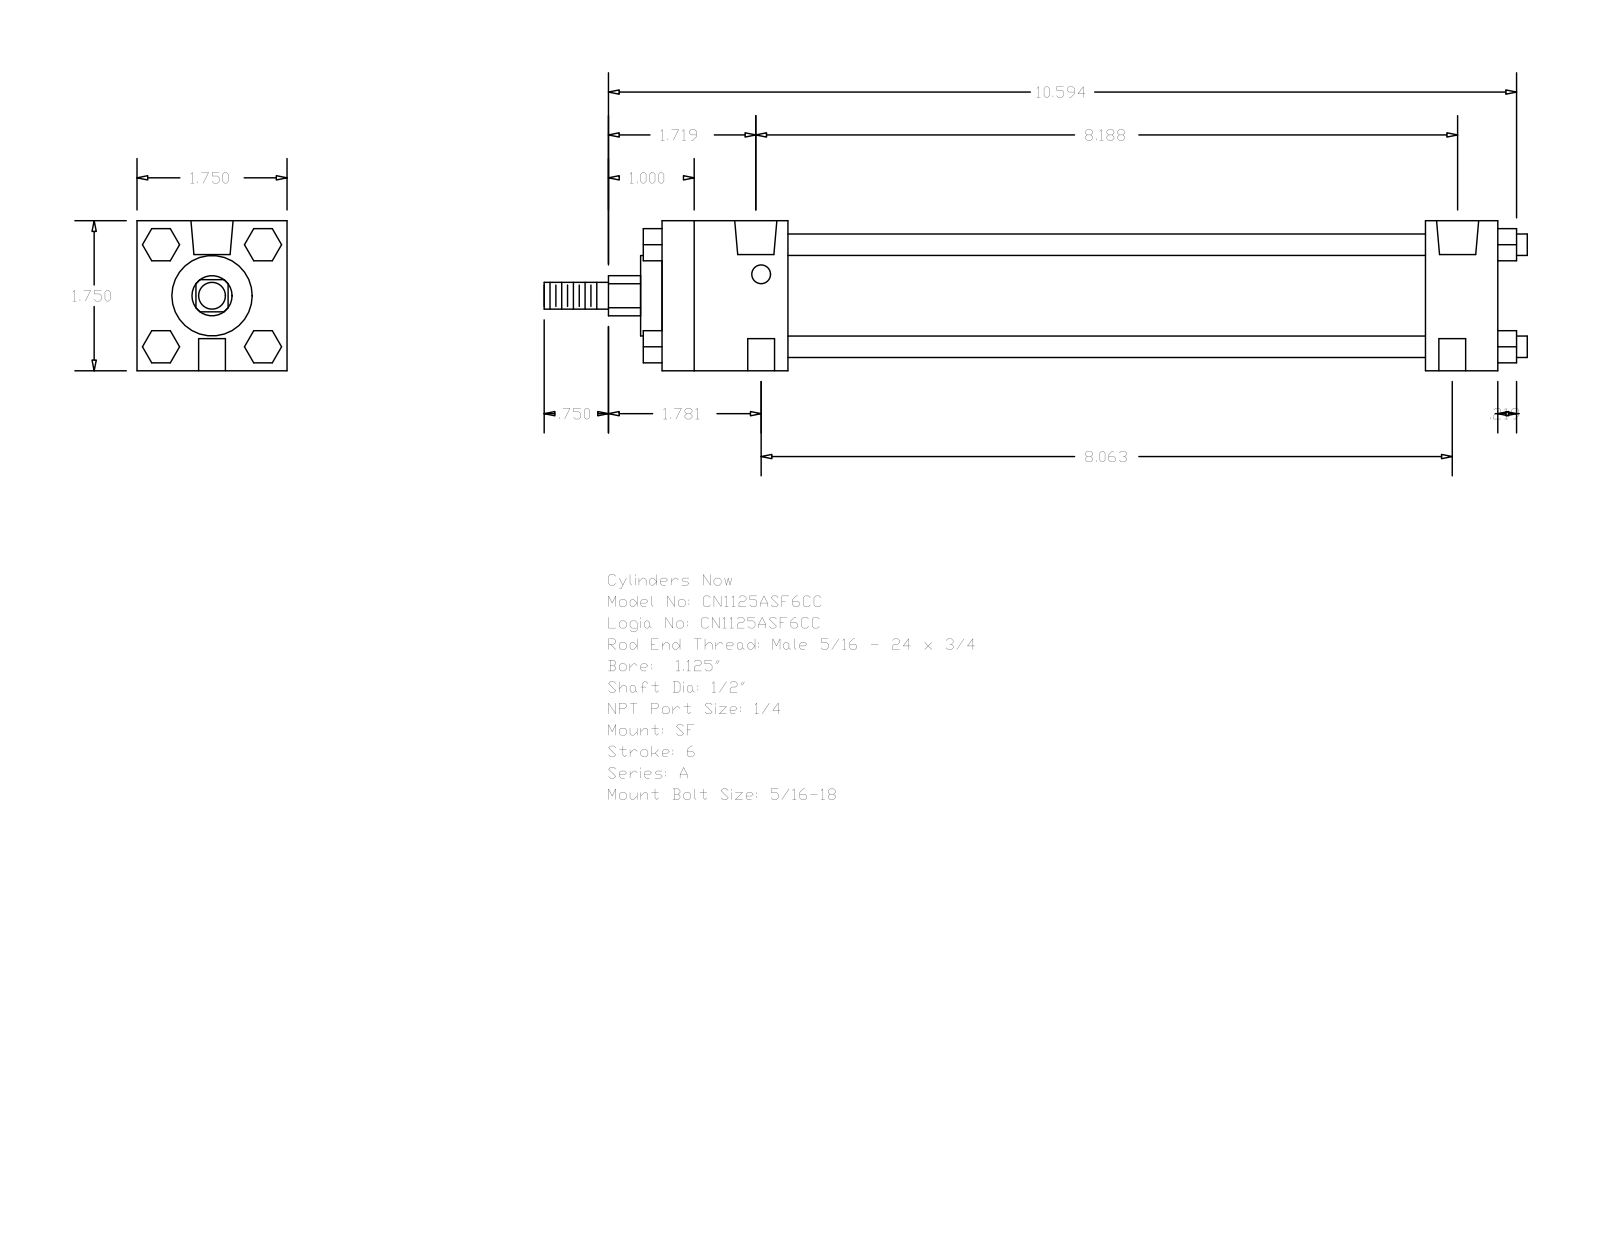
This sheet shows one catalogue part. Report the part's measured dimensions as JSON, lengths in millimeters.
{"part_name": "A_SF__0112_0.5", "step_written_by": "GSSL Pune (CONFIG_CONTROL_DESIGN)", "units": "millimeters", "bodies": {"solids": 0, "faces": 120, "planar": 92, "cylindrical": 28, "other": 0}, "overall_size": [291.31, 44.45, 44.45], "round_holes": [[5.56, 2], [7.94, 2], [12.49, 2]], "round_bosses_or_shafts": [[6.35, 4], [31.88, 1], [23.81, 1], [12.7, 1], [7.94, 1]], "partial_cylinders_radius": [[5.94, 1]], "face_to_face_distances": [44.46, 247.64, 226.21, 21.43, 37.3, 188.91, 210.34, 9.53, 5.59, 5.56], "hole_center_spacings": [204.79, 1.58, 1.59, 206.37, 206.38, 207.96]}
